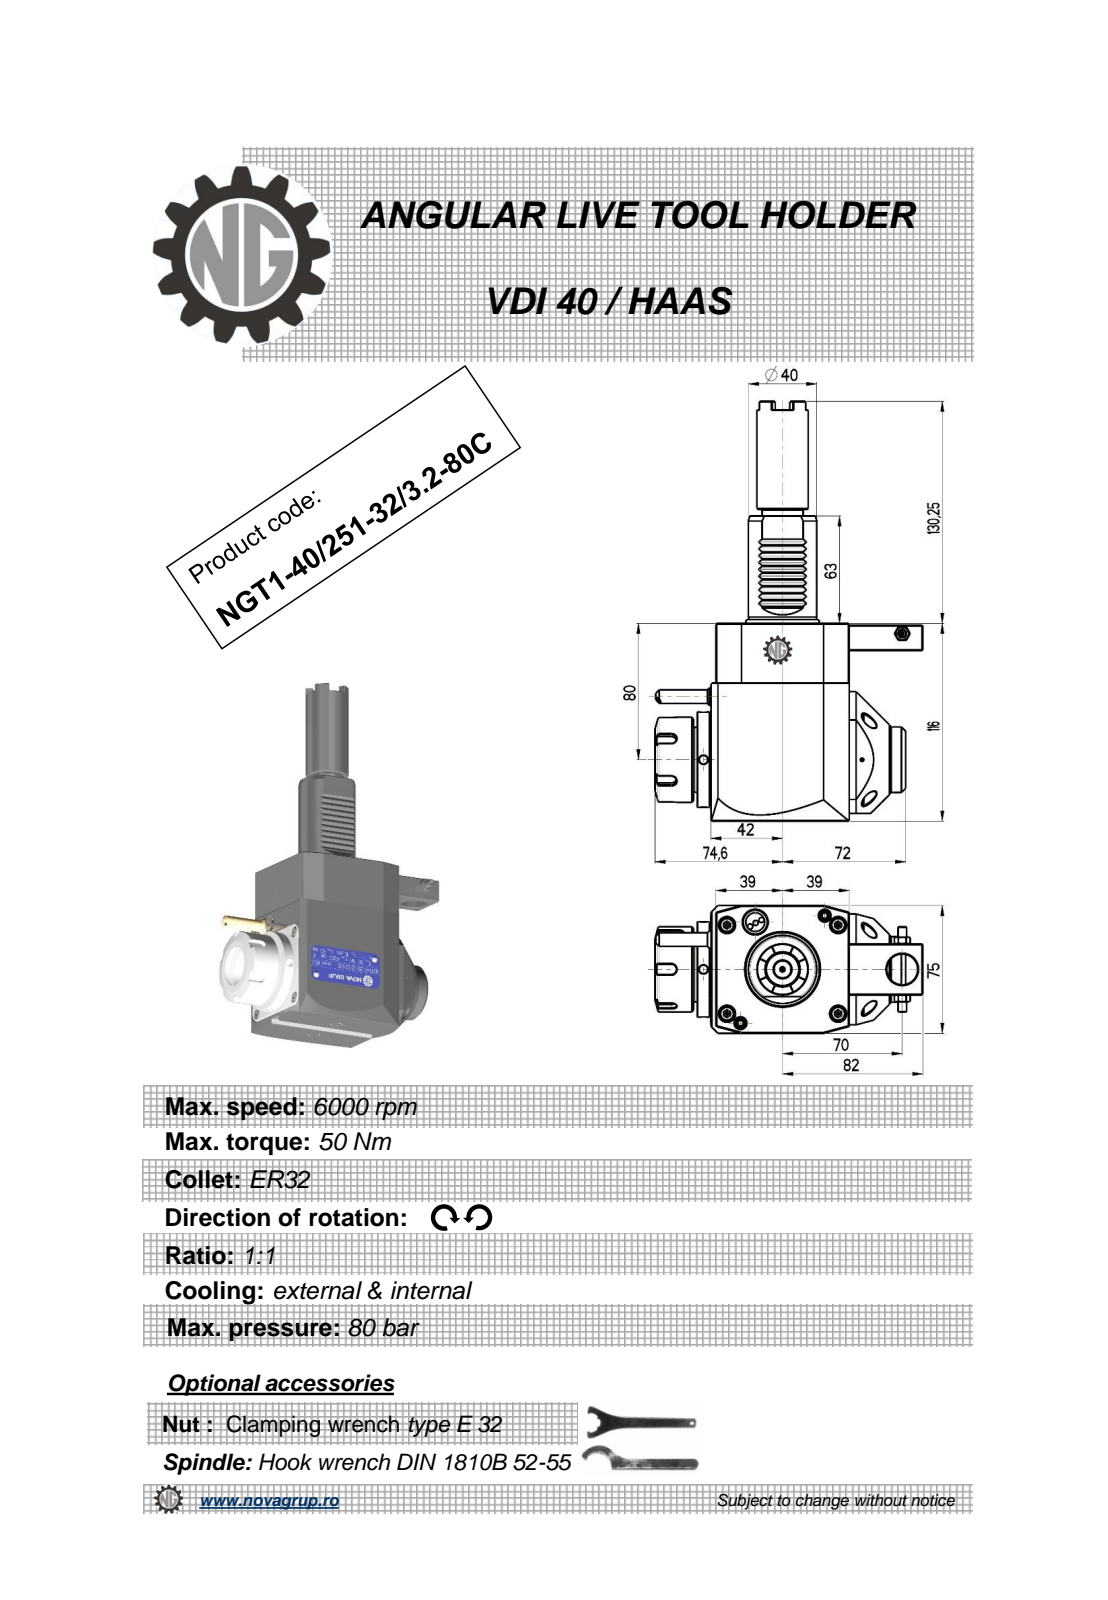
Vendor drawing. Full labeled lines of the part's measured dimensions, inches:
Part name (STEP PRODUCT): NGT1_40_251_32_3_2_80C
STEP written by: PRO/ENGINEER BY PARAMETRIC TECHNOLOGY CORPORATION, 2010280 (CONFIG_CONTROL_DESIGN)
Units: inches
Bodies: 1 solid, 459 faces (220 planar, 89 cylindrical, 150 other)
Overall size (bounding box): 9.695 × 6.165 × 2.953
Volume: 58.34 in³ · Surface area: 126.6 in²
Round holes (diameter × count): ⌀0.197 ×3, ⌀0.118 ×1, ⌀0.165 ×1, ⌀0.374 ×1, ⌀0.709 ×1, ⌀0.787 ×1, ⌀1.063 ×1
Round bosses / shafts (diameter × count): ⌀2.205 ×1, ⌀1.969 ×1, ⌀1.693 ×1, ⌀1.575 ×1, ⌀1.516 ×1, ⌀1.181 ×1, ⌀0.945 ×1, ⌀0.394 ×1
Partial cylindrical surfaces — rounded edges, fillets, slot ends (radius × count): R0.01 ×12, R0.012 ×10, R0.008 ×6, R0.118 ×5, R0.02 ×1, R1.575 ×1
Main face-to-face distances: 2.953, 4.567, 3.189, 3.071, 0.118, 4.37, 0.039, 0.11, 3.181, 0.886
Hole centre spacings: 1.558, 1.611, 1.821, 2.756, 2.854, 4.577, 5.425
